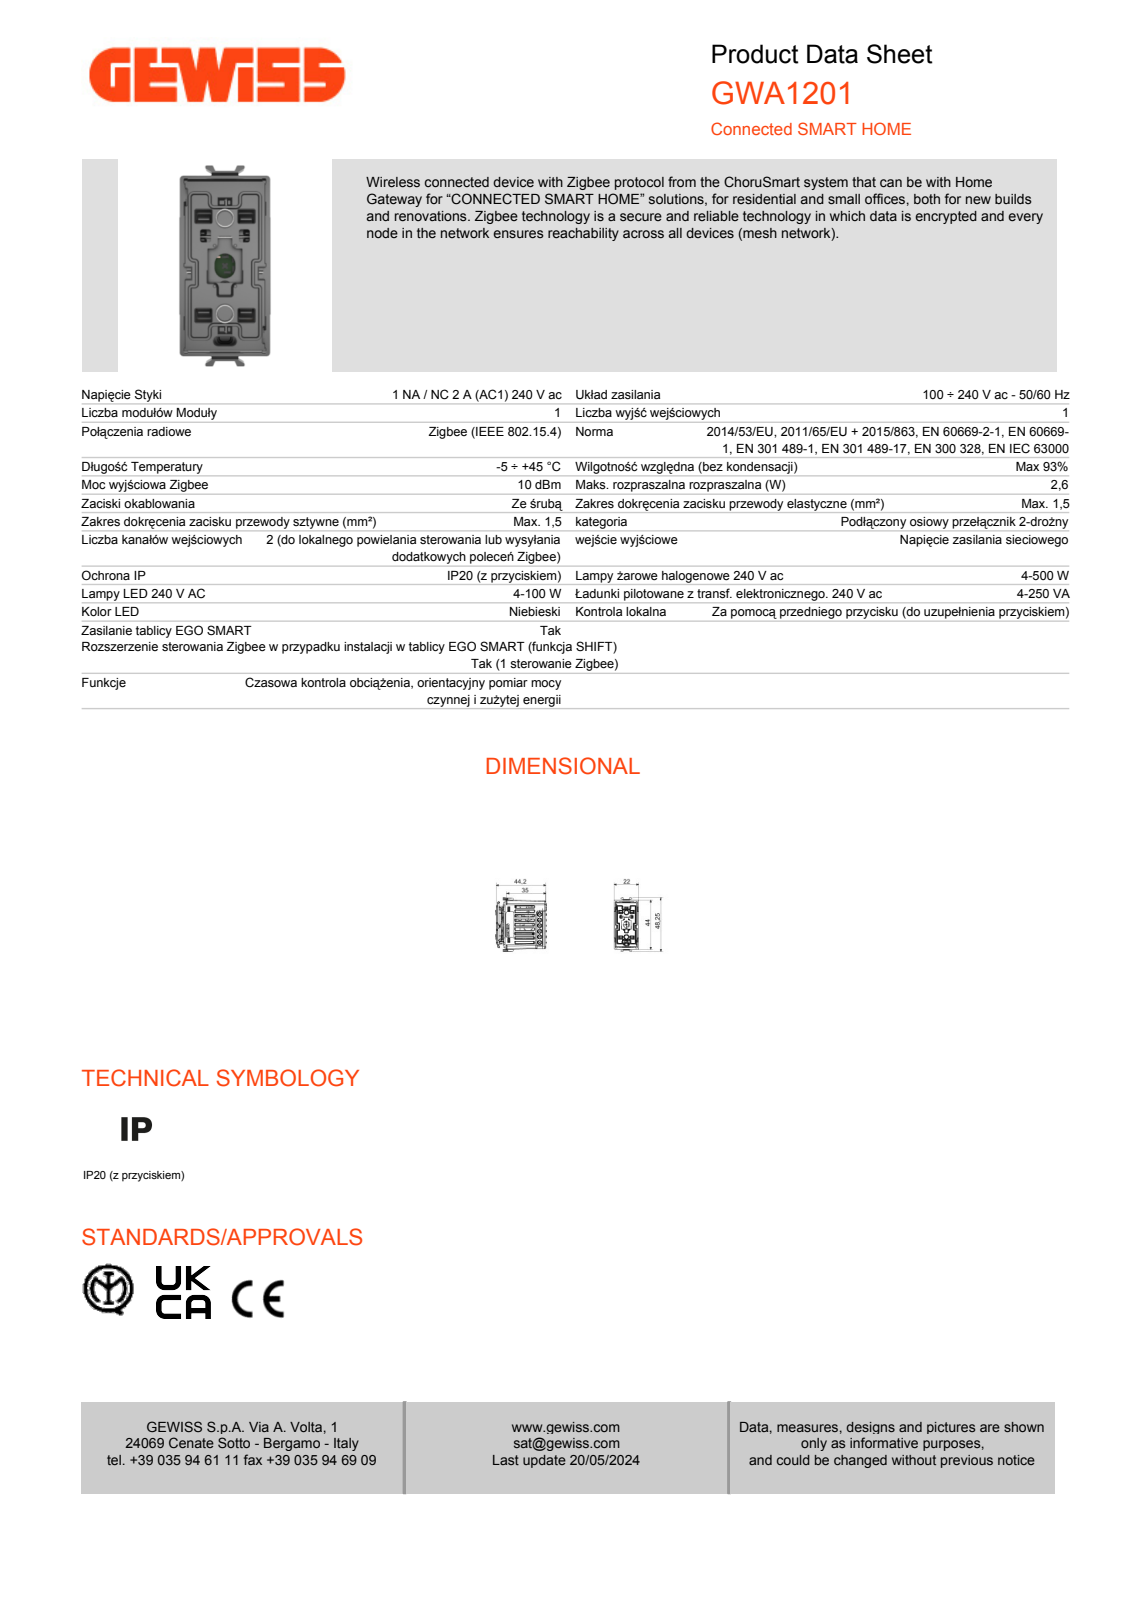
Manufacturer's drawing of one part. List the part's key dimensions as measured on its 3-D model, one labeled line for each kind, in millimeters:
Part name (STEP PRODUCT): GWA1201
STEP written by: CATIA V5 STEP AP214 v1 (AUTOMOTIVE_DESIGN)
Units: millimetres
Bodies: 2 solids, 2569 faces (1233 planar, 797 cylindrical, 539 other)
Overall size (bounding box): 48.25 × 44.55 × 22
Volume: 32 013 mm³ · Surface area: 11 091 mm²
Round holes (diameter × count): ⌀3 ×6, ⌀1.99 ×2, ⌀2.5 ×1
Partial cylindrical surfaces — rounded edges, fillets, slot ends (radius × count): R0.2 ×289, R0.5 ×120, R0.3 ×86, R0.1 ×73, R1.7 ×17, R1.2 ×14, R1 ×11, R0.9 ×4
Main face-to-face distances: 1.5, 1.3, 5.2, 3.9, 1, 6.4, 41.7, 6.7, 4.9, 5.4
Hole centre spacings: 5, 10, 15, 20, 1.2, 12.47, 12.81, 13.62
